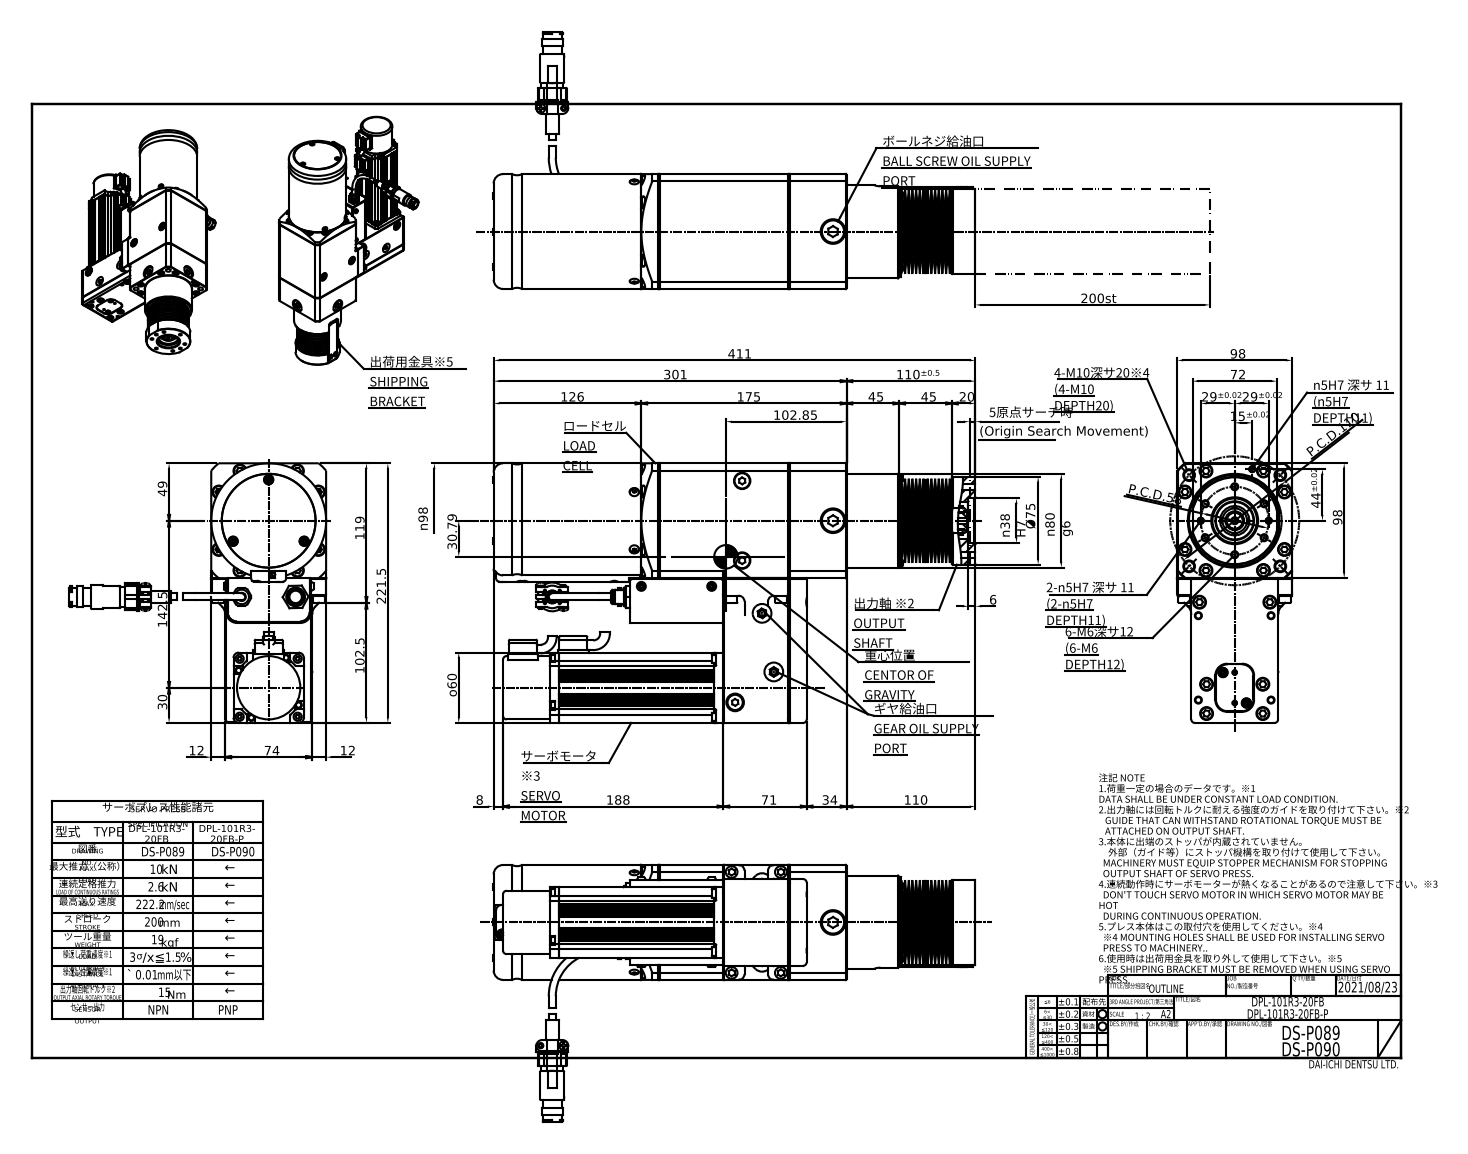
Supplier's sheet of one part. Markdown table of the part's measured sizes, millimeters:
| quantity | value |
| --- | --- |
| part name | DPL-101R3-20FB(DS-P089)_OUTLINE_20210830 |
| STEP written by | Autodesk Inventor 2021 (AUTOMOTIVE_DESIGN) |
| units | millimeters |
| bodies | 16 solids, 2931 faces (1728 planar, 606 cylindrical, 597 other) |
| overall size | 411.2 × 221.5 × 219.62 |
| volume | 4 439 000 mm³ |
| surface area | 437 210 mm² |
| round holes (diameter × count) | 11 × 15, 5 × 14, 8 × 10, 1.1 × 7, 8.5 × 6, 1.2 × 4, 4.5 × 4, 3.3 × 3, 2.5 × 2, 4.1 × 2, 4.3 × 2, 16 × 2 |
| round bosses / shafts (diameter × count) | 10 × 18, 5.5 × 11, 1.55 × 7, 1 × 7, 7 × 4, 4 × 4, 1.4 × 4, 13 × 3 |
| partial cylindrical surfaces (radius × count) | 1 × 48, 0.75 × 38, 0.5 × 34, 10 × 16, 3 × 10, 5 × 10, 0.4 × 8, 0.9 × 4 |
| main face-to-face distances | 98, 86, 12, 19, 79, 221.5, 7, 60, 67, 48.5 |
| hole center spacings | 3, 5.2, 49, 14.82, 55, 63.49, 77.78, 82.59 |
